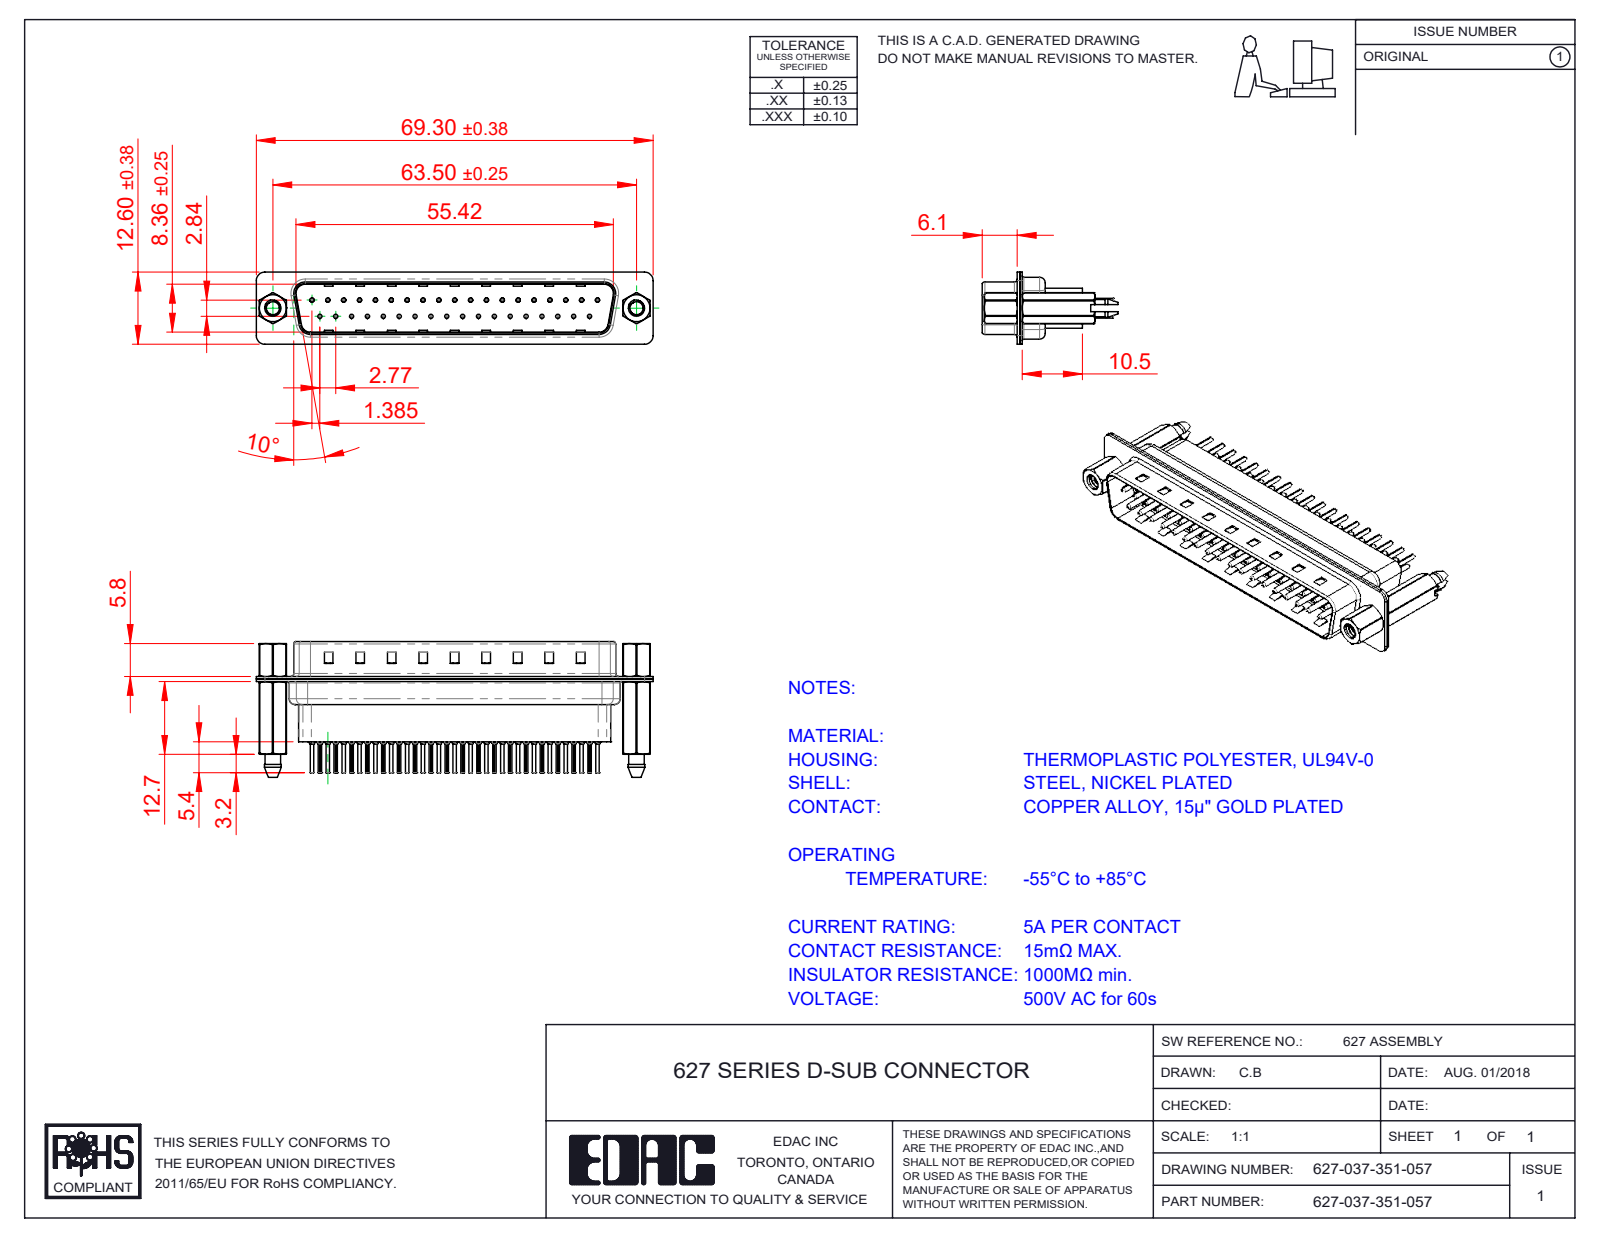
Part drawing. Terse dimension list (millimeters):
name: 627 Housing_37 HP; 627 4-40 Threaded Boardlock_HP51; 627 4-40 Hex Standoff; 627 Shell Rear_37 Contacts (+4 more)
written by: SolidWorks 2020 (CONFIG_CONTROL_DESIGN)
unit: mm
bodies: 44 solids, 4272 faces (1145 planar, 1648 cylindrical, 1479 other)
size: 69.3 × 23.6 × 12.6
volume: 5 848 mm³; area: 14 927 mm²
holes: 37× ⌀0.2, 37× ⌀0.35, 37× ⌀1.1, 37× ⌀1.6, 2× ⌀2.26, 2× ⌀2.29, 2× ⌀4, 2× ⌀4.8
bosses: 37× ⌀2, 37× ⌀1.5, 37× ⌀0.75, 37× ⌀0.6, 2× ⌀4.9, 2× ⌀2.79
rounds: 74× R0.1, 18× R1.5, 12× R2, 10× R1.6, 8× R0.5, 4× R0.25, 4× R0.6, 4× R0.65
face distances: 0.4, 0.82, 9.58, 0.45, 0.68, 7.68, 1.5, 1.08, 8.08, 8.76
hole spacings: 3.16, 2.77, 5.54, 8.31, 5.04, 10.1, 11.08, 12.78
